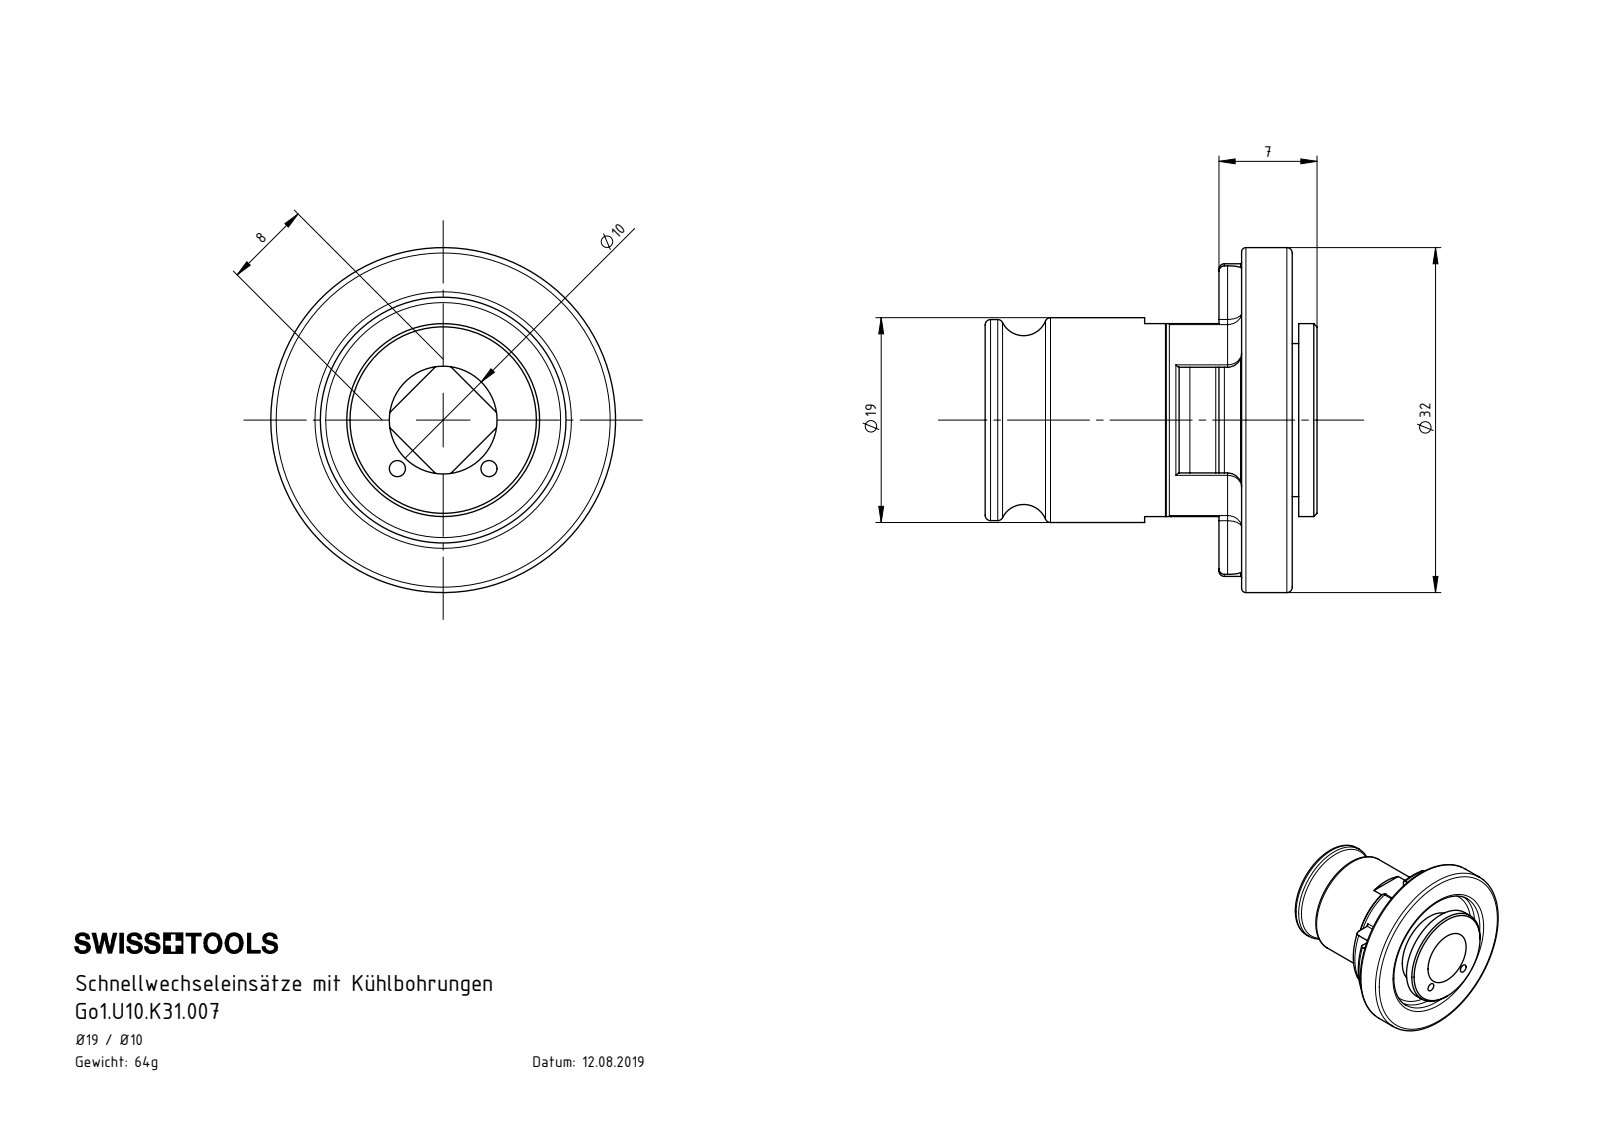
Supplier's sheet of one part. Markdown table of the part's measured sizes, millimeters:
| quantity | value |
| --- | --- |
| part name | Go1.U10.K31.007 |
| STEP written by | SolidWorks 2017 (AUTOMOTIVE_DESIGN) |
| units | millimeters |
| bodies | 1 solid, 117 faces (36 planar, 34 cylindrical, 47 other) |
| overall size | 32 × 32 × 30.8 |
| volume | 8 100 mm³ |
| surface area | 5 141 mm² |
| round holes (diameter × count) | 1.5 × 2, 10 × 1, 11.4 × 1, 22.8 × 1 |
| round bosses / shafts (diameter × count) | 32 × 1, 19 × 1, 18.65 × 1, 18.52 × 1, 17.9 × 1, 14.2 × 1 |
| partial cylindrical surfaces (radius × count) | 0.5 × 8, 1.3 × 4, 12.4 × 1, 14.5 × 1 |
| main face-to-face distances | 2.35, 4.7, 7, 4.65, 2.3, 23.8, 26.15, 28.5, 30.8, 29.1 |
| hole center spacings | 6.19, 8.5 |
